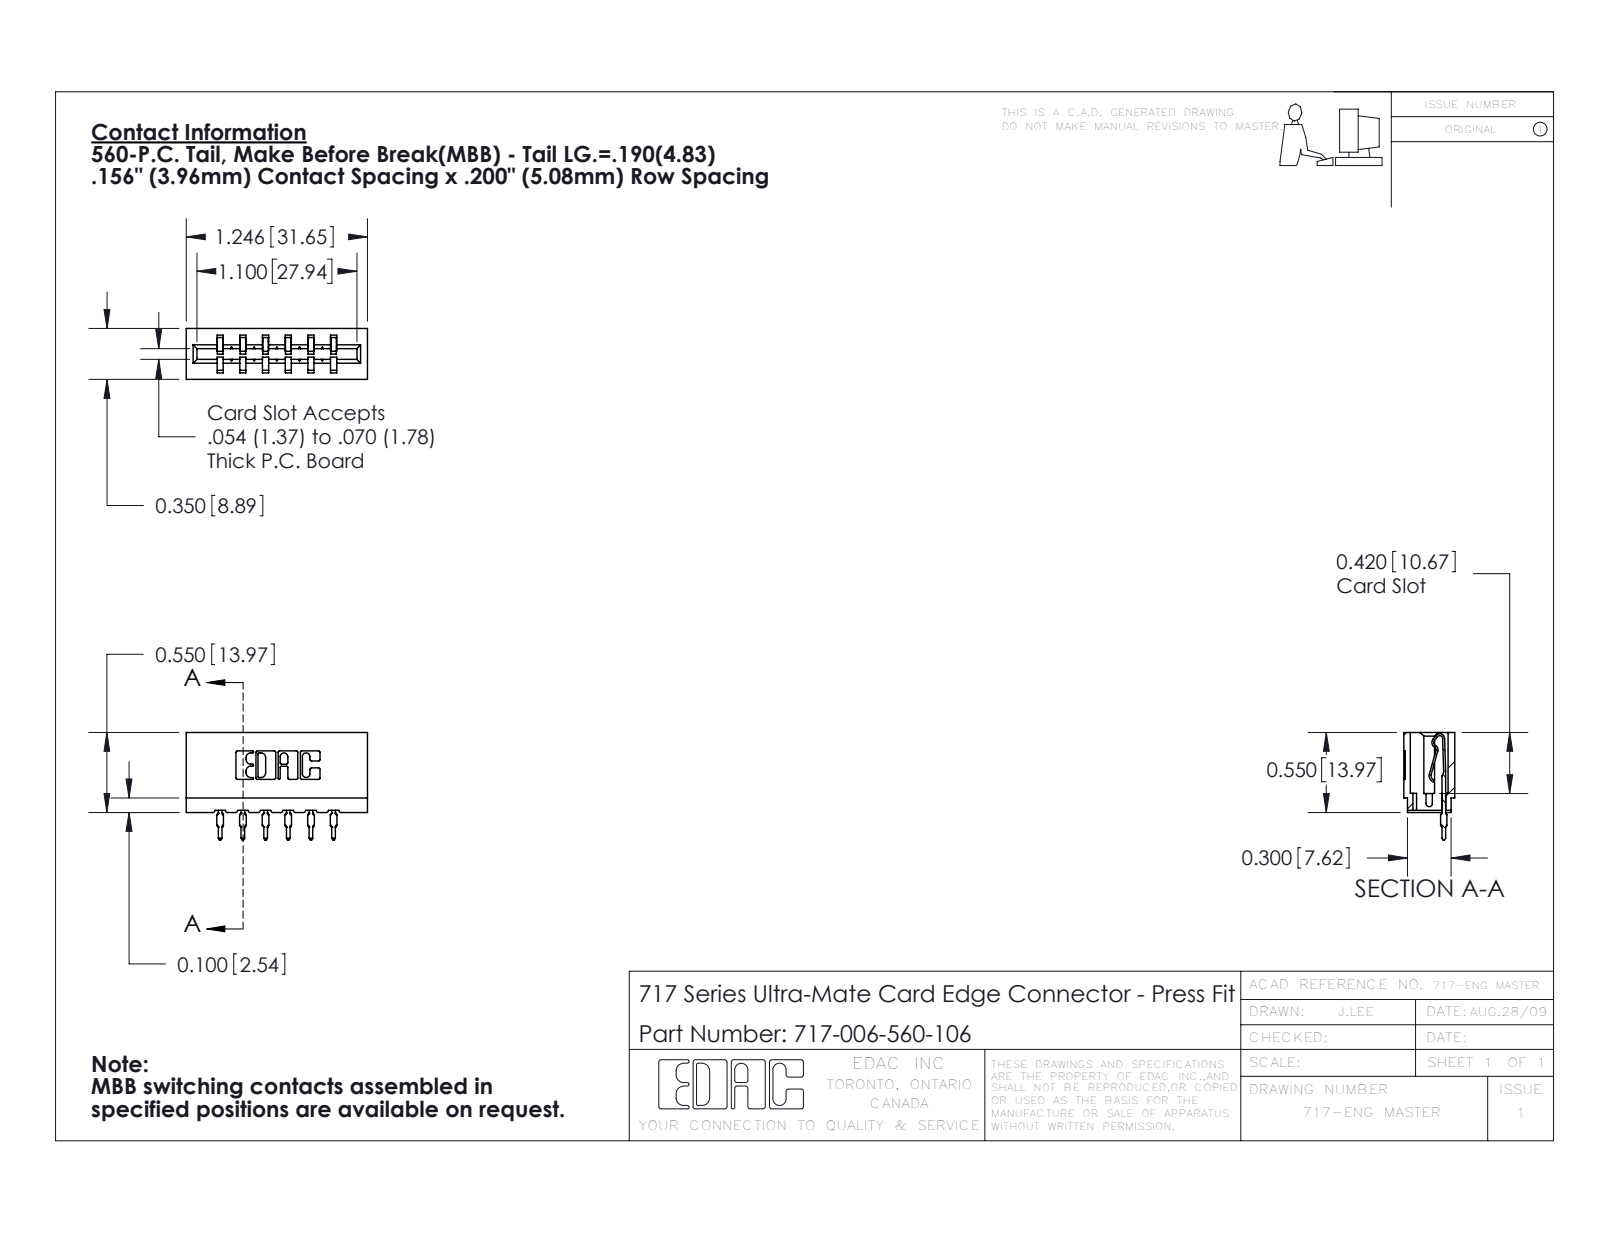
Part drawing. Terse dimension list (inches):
name: 745-292-001_560; 717 Part_Insulator Option - 06; 717-006-560-106
written by: SolidWorks 2016 (CONFIG_CONTROL_DESIGN)
unit: in
bodies: 7 solids, 826 faces (492 planar, 178 cylindrical, 156 other)
size: 1.246 × 0.739 × 0.35
volume: 0.174 in³; area: 5.759 in²
rounds: 22× R0.01, 12× R0.015, 12× R0.021, 6× R0.007, 6× R0.031, 4× R0.005, 4× R0.011, 3× R0.026
face distances: 0.212, 0.156, 0.138, 0.35, 0.198, 0.312, 0.624, 0.042, 0.312, 0.468
